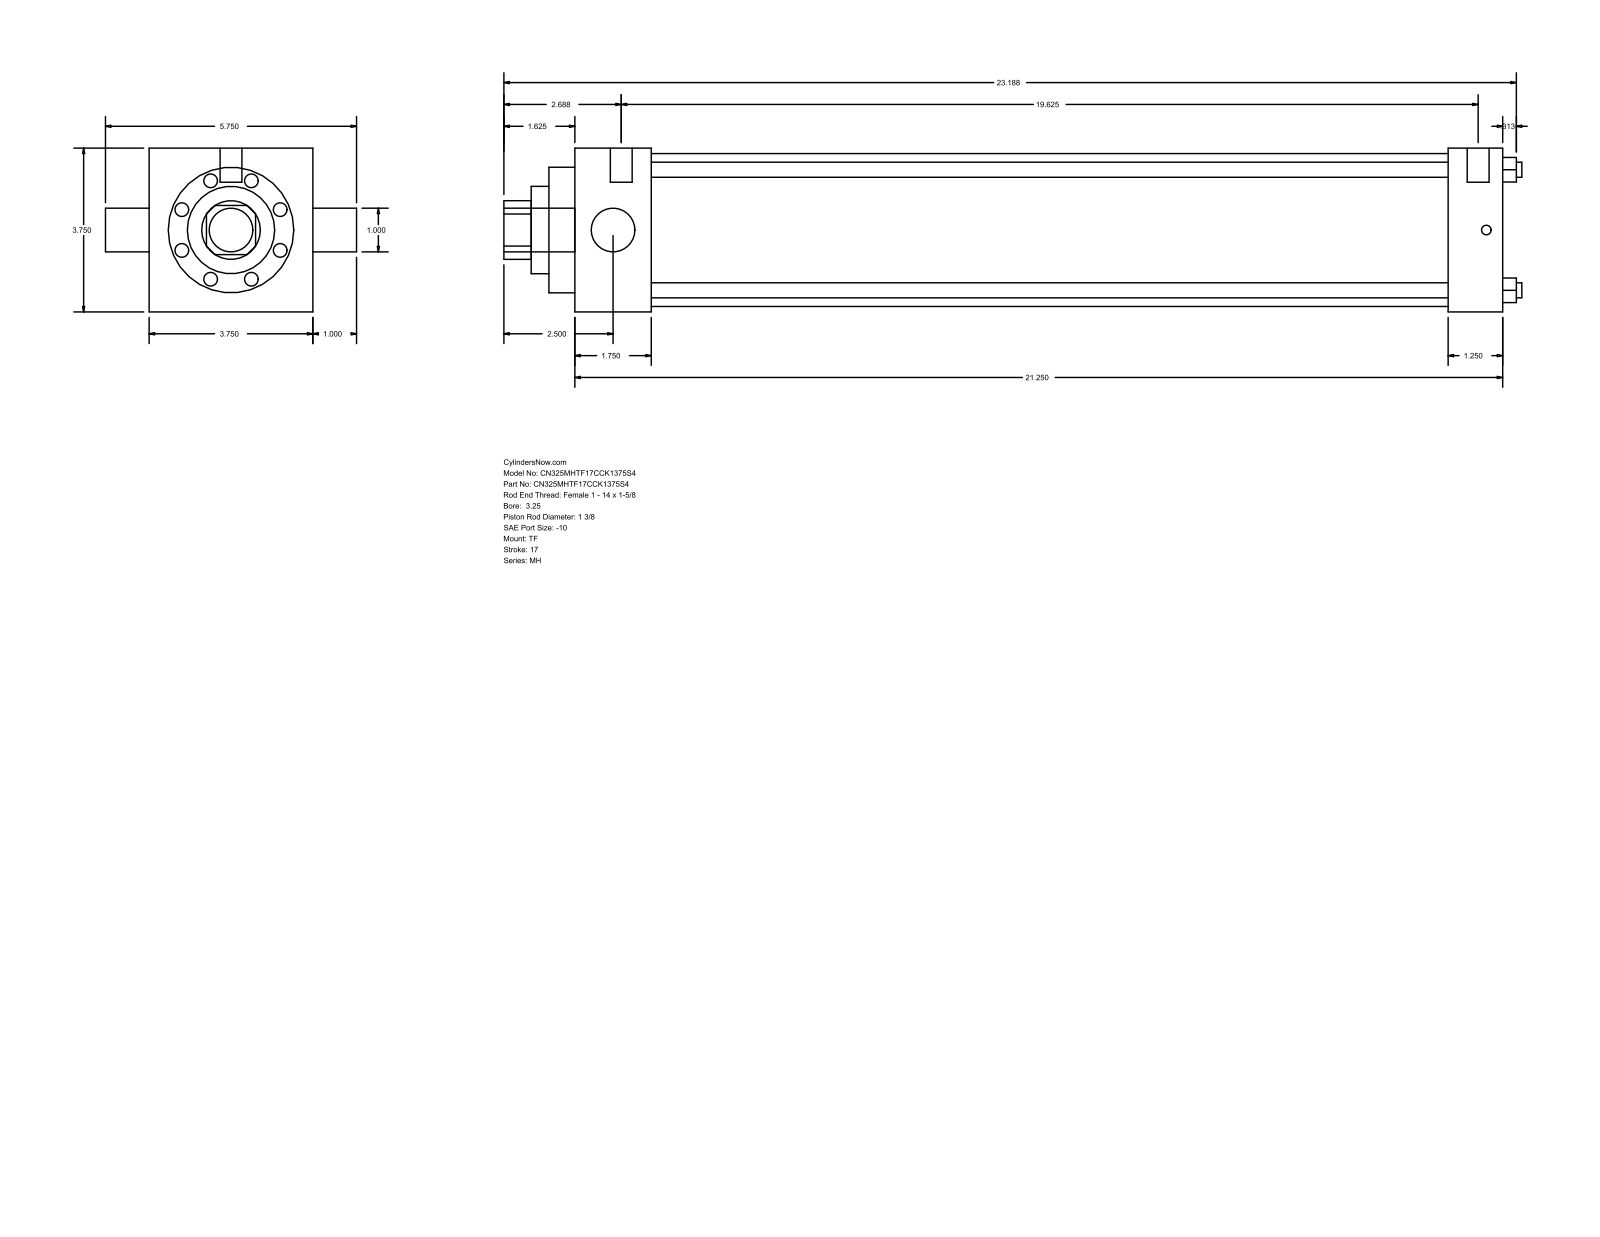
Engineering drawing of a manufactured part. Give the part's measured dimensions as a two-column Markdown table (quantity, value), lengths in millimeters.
| quantity | value |
| --- | --- |
| part name | MH_TF__0325_1.375 |
| STEP written by | GSSL Pune (CONFIG_CONTROL_DESIGN) |
| units | millimeters |
| bodies | 0 solids, 86 faces (61 planar, 25 cylindrical, 0 other) |
| overall size | 592.14 × 146.05 × 95.25 |
| round holes (diameter × count) | 8.76 × 4, 25.4 × 1, 34.92 × 1, 50.8 × 1, 73.03 × 1, 88.9 × 1 |
| round bosses / shafts (diameter × count) | 5.56 × 3, 12.7 × 2, 25.4 × 1 |
| partial cylindrical surfaces (radius × count) | 17.06 × 1 |
| main face-to-face distances | 95.24, 539.75, 44.45, 508, 463.55, 495.3, 31.75, 15.08, 59.53, 523.08 |
| hole center spacings | 49.57, 70.1, 99.14 |
